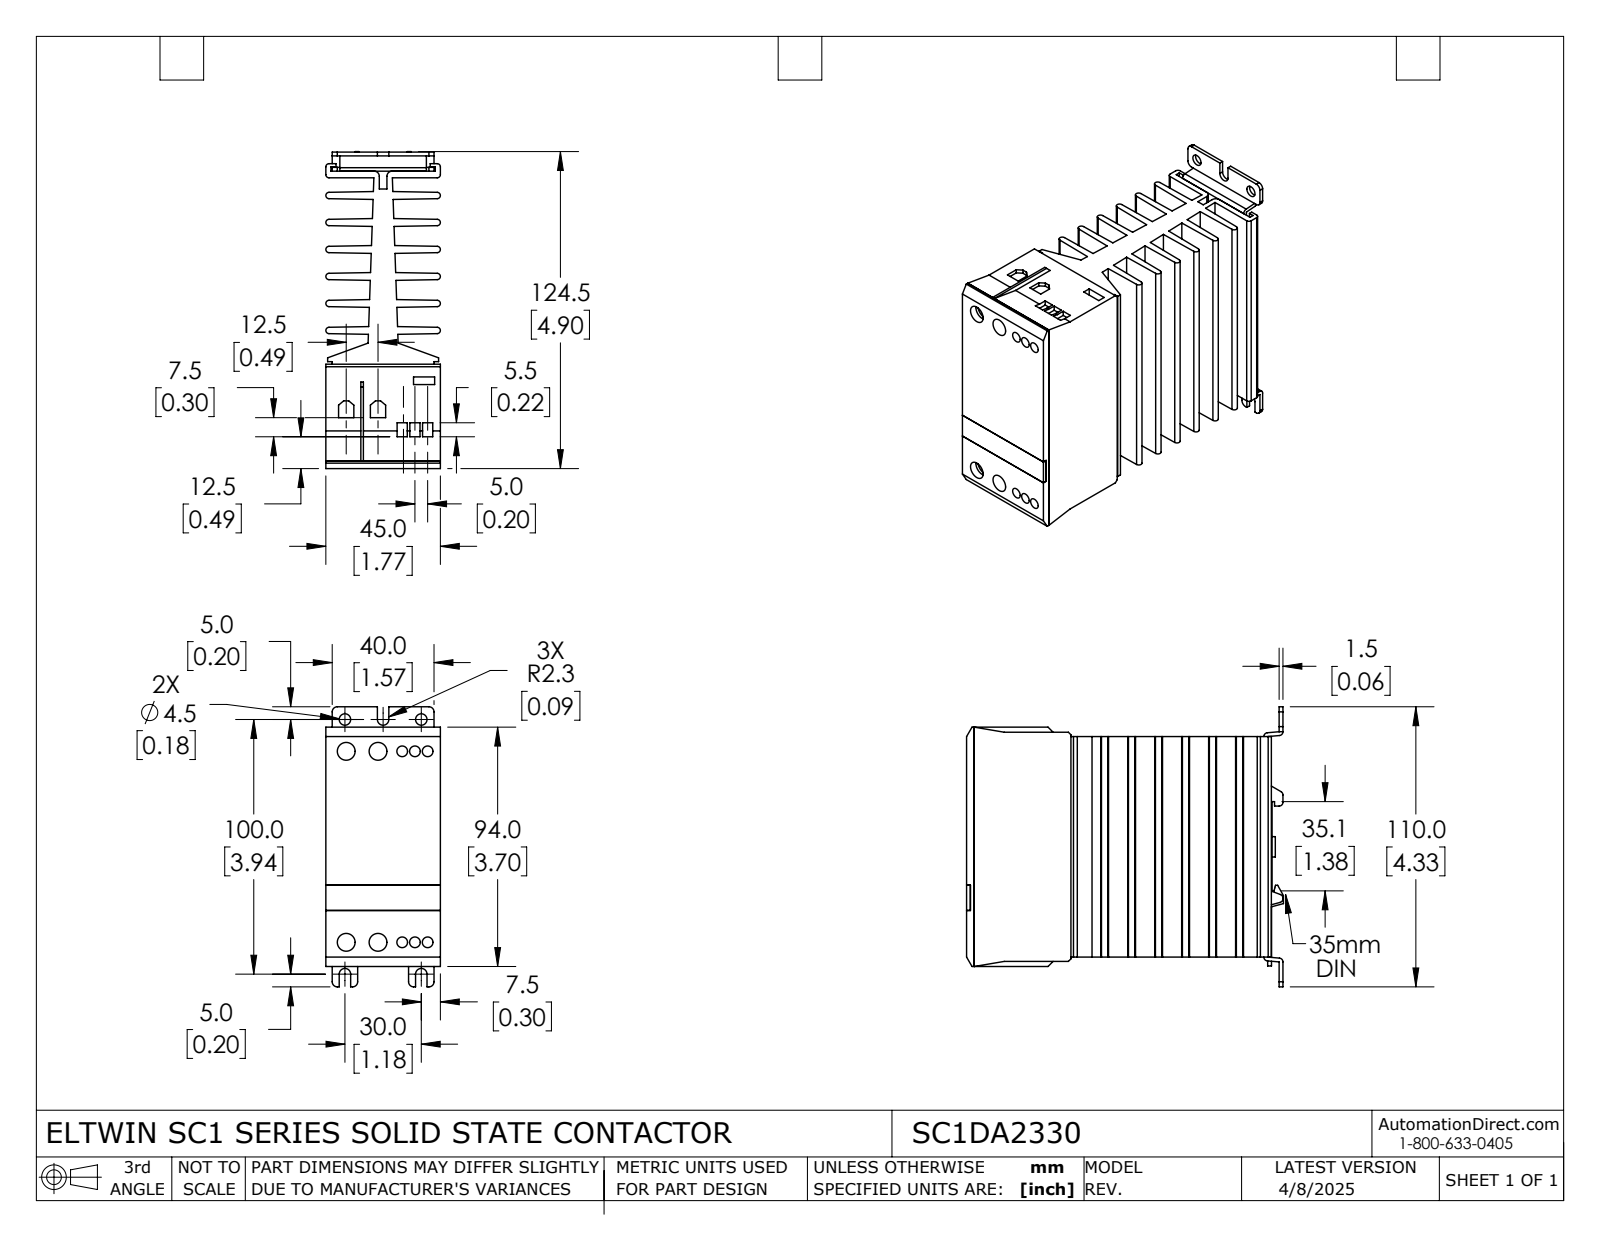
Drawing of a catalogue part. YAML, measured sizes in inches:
part_name: "SC1DA2330"
step_written_by: "SolidWorks 2021 (AUTOMOTIVE_DESIGN)"
units: inches
bodies: {solids: 7, faces: 391, planar: 284, cylindrical: 107, other: 0}
overall_size: [4.902, 4.331, 1.772]
volume: 18.87
surface_area: 165.4
round_holes:
  - {diameter: 0.165, count: 6}
  - {diameter: 0.173, count: 6}
  - {diameter: 0.276, count: 4}
  - {diameter: 0.177, count: 2}
  - {diameter: 0.315, count: 2}
round_bosses_or_shafts:
  - {diameter: 0.315, count: 3}
partial_cylinders:
  - {radius: 0.079, count: 18}
  - {radius: 0.049, count: 16}
  - {radius: 0.059, count: 10}
  - {radius: 0.051, count: 4}
  - {radius: 0.089, count: 3}
face_to_face_distances: [0.417, 0.835, 0.127, 1.252, 0.29, 0.544, 0.707, 0.962, 1.669, 1.125]
hole_center_spacings: [2.953, 0.197, 2.959, 0.374, 0.394, 0.492, 0.502, 0.571]
